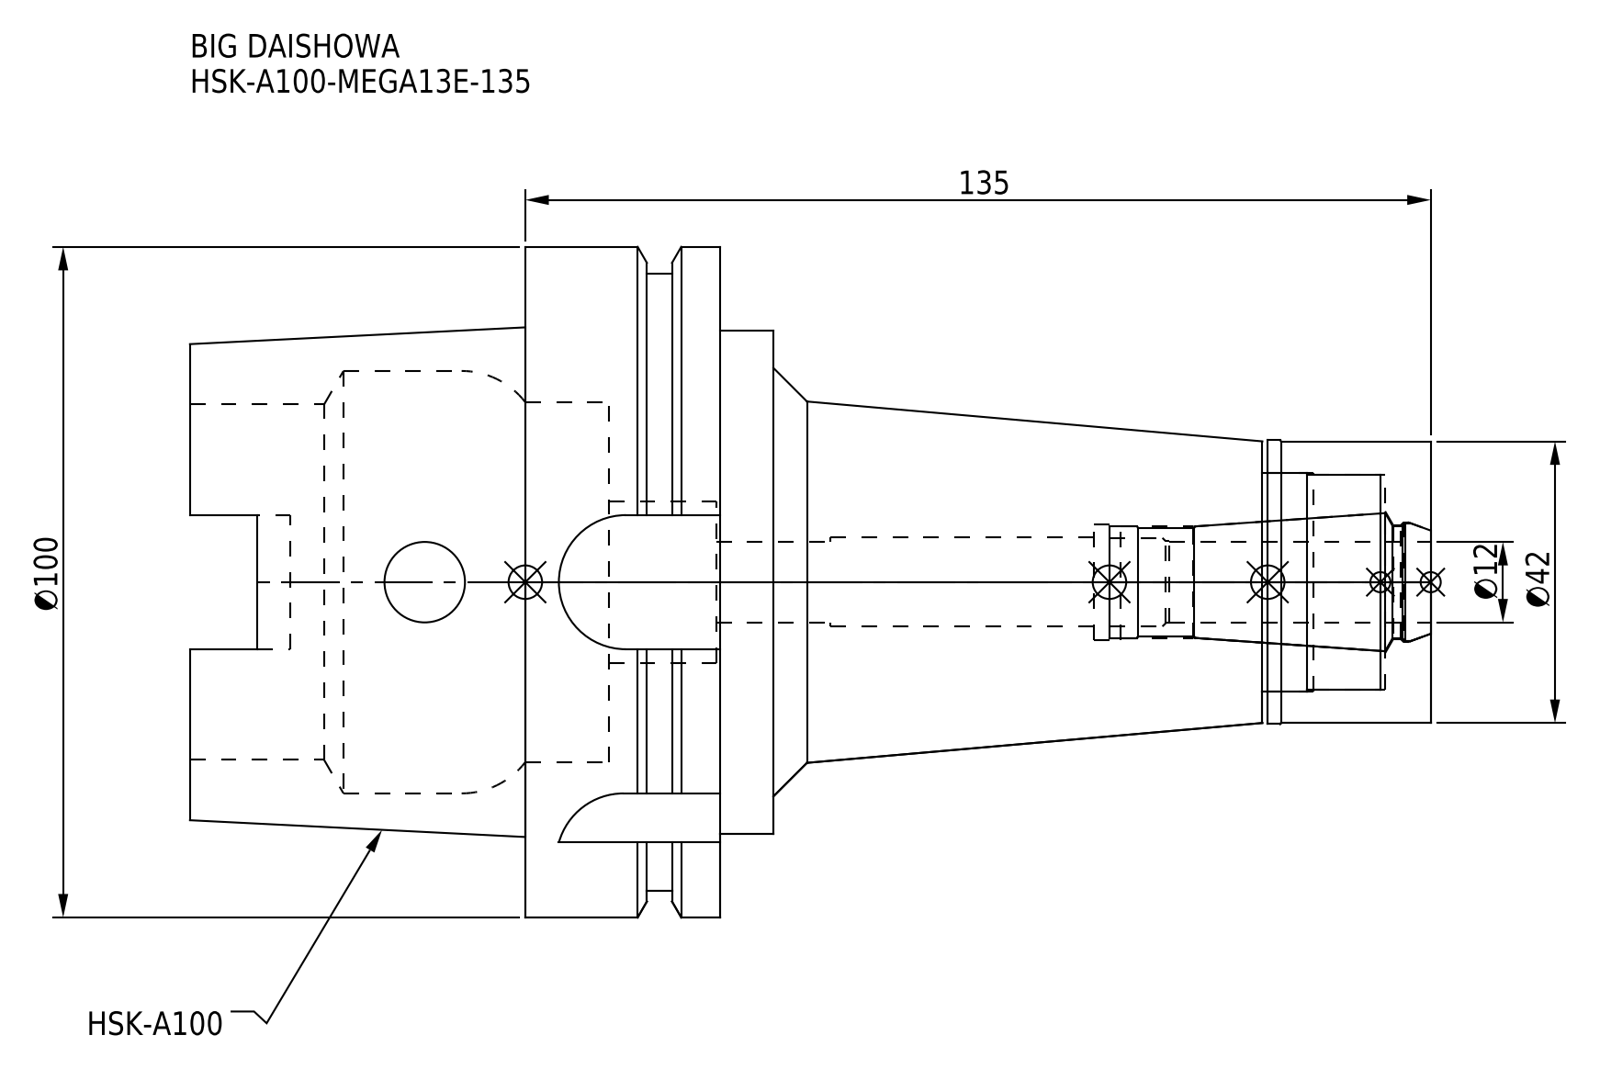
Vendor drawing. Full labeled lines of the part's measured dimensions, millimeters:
Part name (STEP PRODUCT): MEN13_1.stp; DXF_TEMP_ASSY_ASM_4_ASM.stp; HSK-A100-MEGA13E-135-120-FreeParts; HSK-A100-MEGA13E-135 (+3 more)
STEP written by: SolidWorks 2019 (CONFIG_CONTROL_DESIGN)
Units: millimetres
Bodies: 2 solids, 126 faces (42 planar, 56 cylindrical, 28 other)
Overall size (bounding box): 185 × 100 × 100
Volume: 439 752 mm³ · Surface area: 75 506 mm²
Round holes (diameter × count): ⌀12 ×2, ⌀13.3 ×1, ⌀16.6 ×1, ⌀17 ×1, ⌀17.2 ×1, ⌀17.9 ×1, ⌀24 ×1, ⌀32 ×1, ⌀32.5 ×1, ⌀53 ×1, ⌀53.8 ×1, ⌀63 ×1
Round bosses / shafts (diameter × count): ⌀100 ×1, ⌀92 ×1, ⌀75 ×1, ⌀42.3 ×1, ⌀42 ×1
Partial cylindrical surfaces — rounded edges, fillets, slot ends (radius × count): R4.88 ×4, R10 ×4
Main face-to-face distances: 29, 16.55, 12.45, 8, 24.55, 37, 98, 106, 122.55, 135
